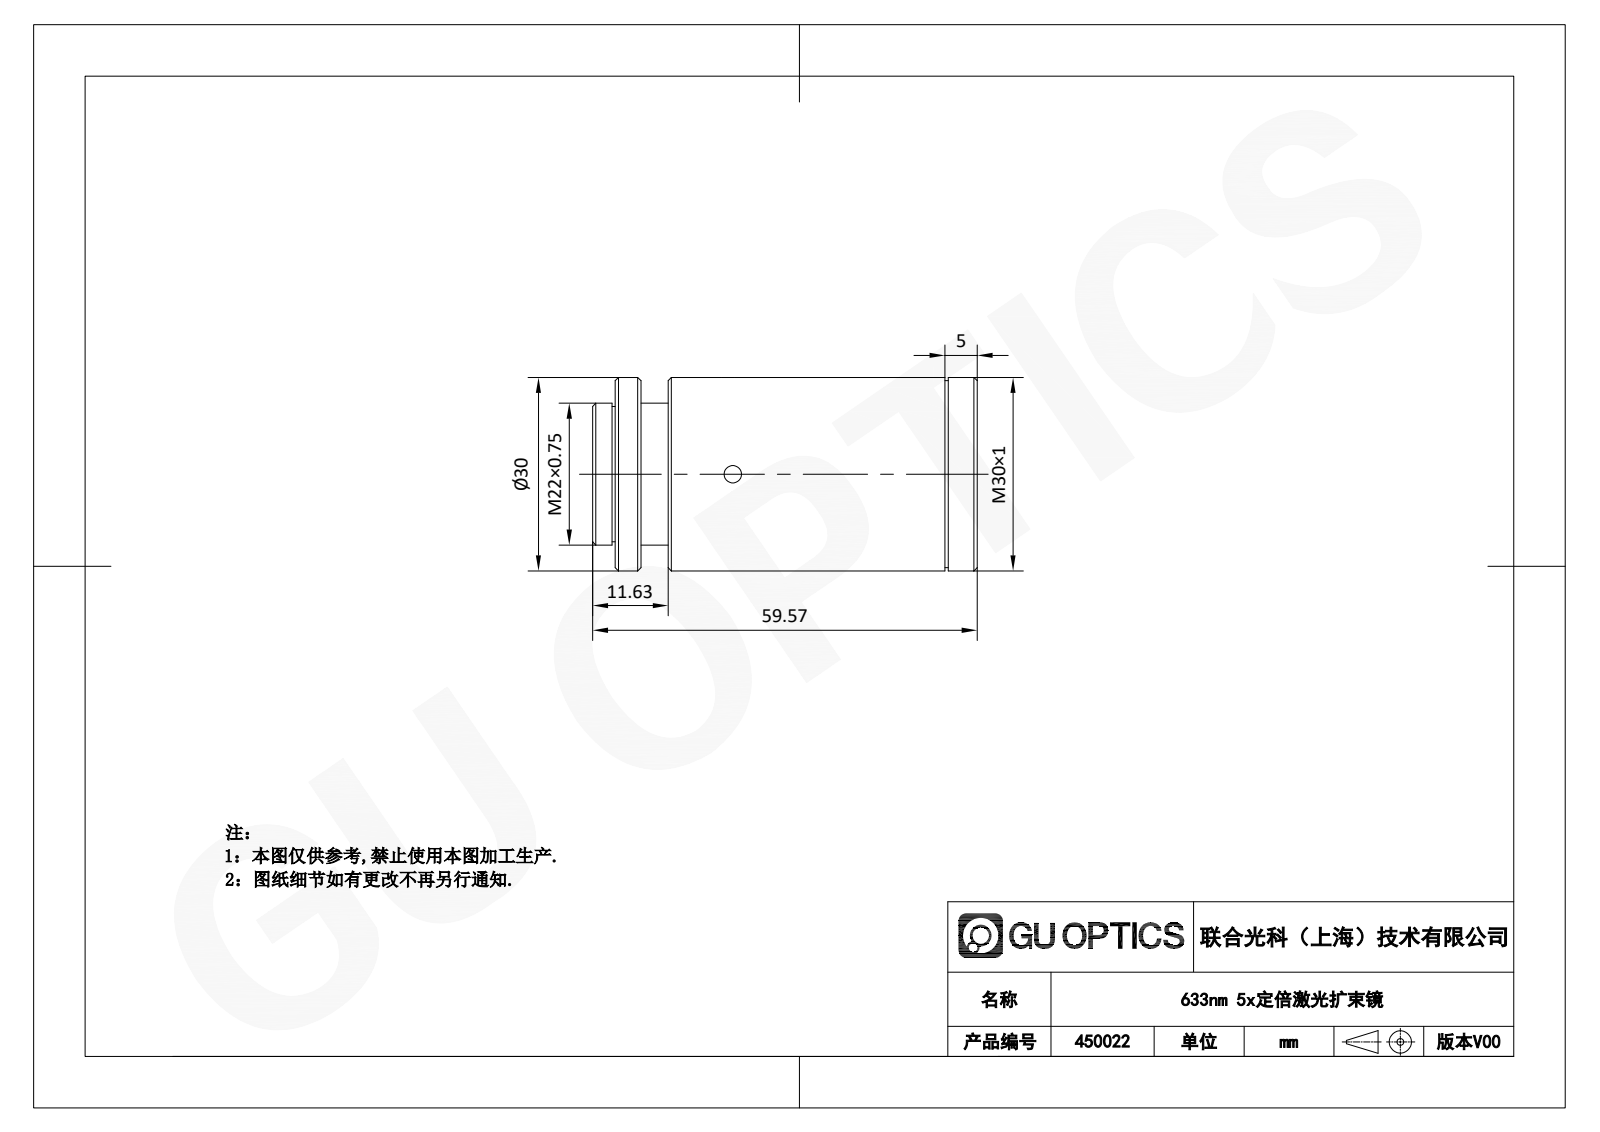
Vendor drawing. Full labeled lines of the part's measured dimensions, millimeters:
Part name (STEP PRODUCT): 450022
STEP written by: SolidWorks 2020 (CONFIG_CONTROL_DESIGN)
Units: millimetres
Bodies: 1 solid, 44 faces (12 planar, 22 cylindrical, 10 other)
Overall size (bounding box): 59.57 × 30 × 30
Volume: 38 599 mm³ · Surface area: 8 338 mm²
Round holes (diameter × count): ⌀2 ×1, ⌀8 ×1, ⌀18 ×1, ⌀20 ×1
Round bosses / shafts (diameter × count): ⌀30 ×1, ⌀29 ×1, ⌀22 ×1, ⌀21 ×1
Main face-to-face distances: 2, 57.57, 1, 56.07, 52.07, 1.5, 2.5, 54.07, 3.5, 59.57
